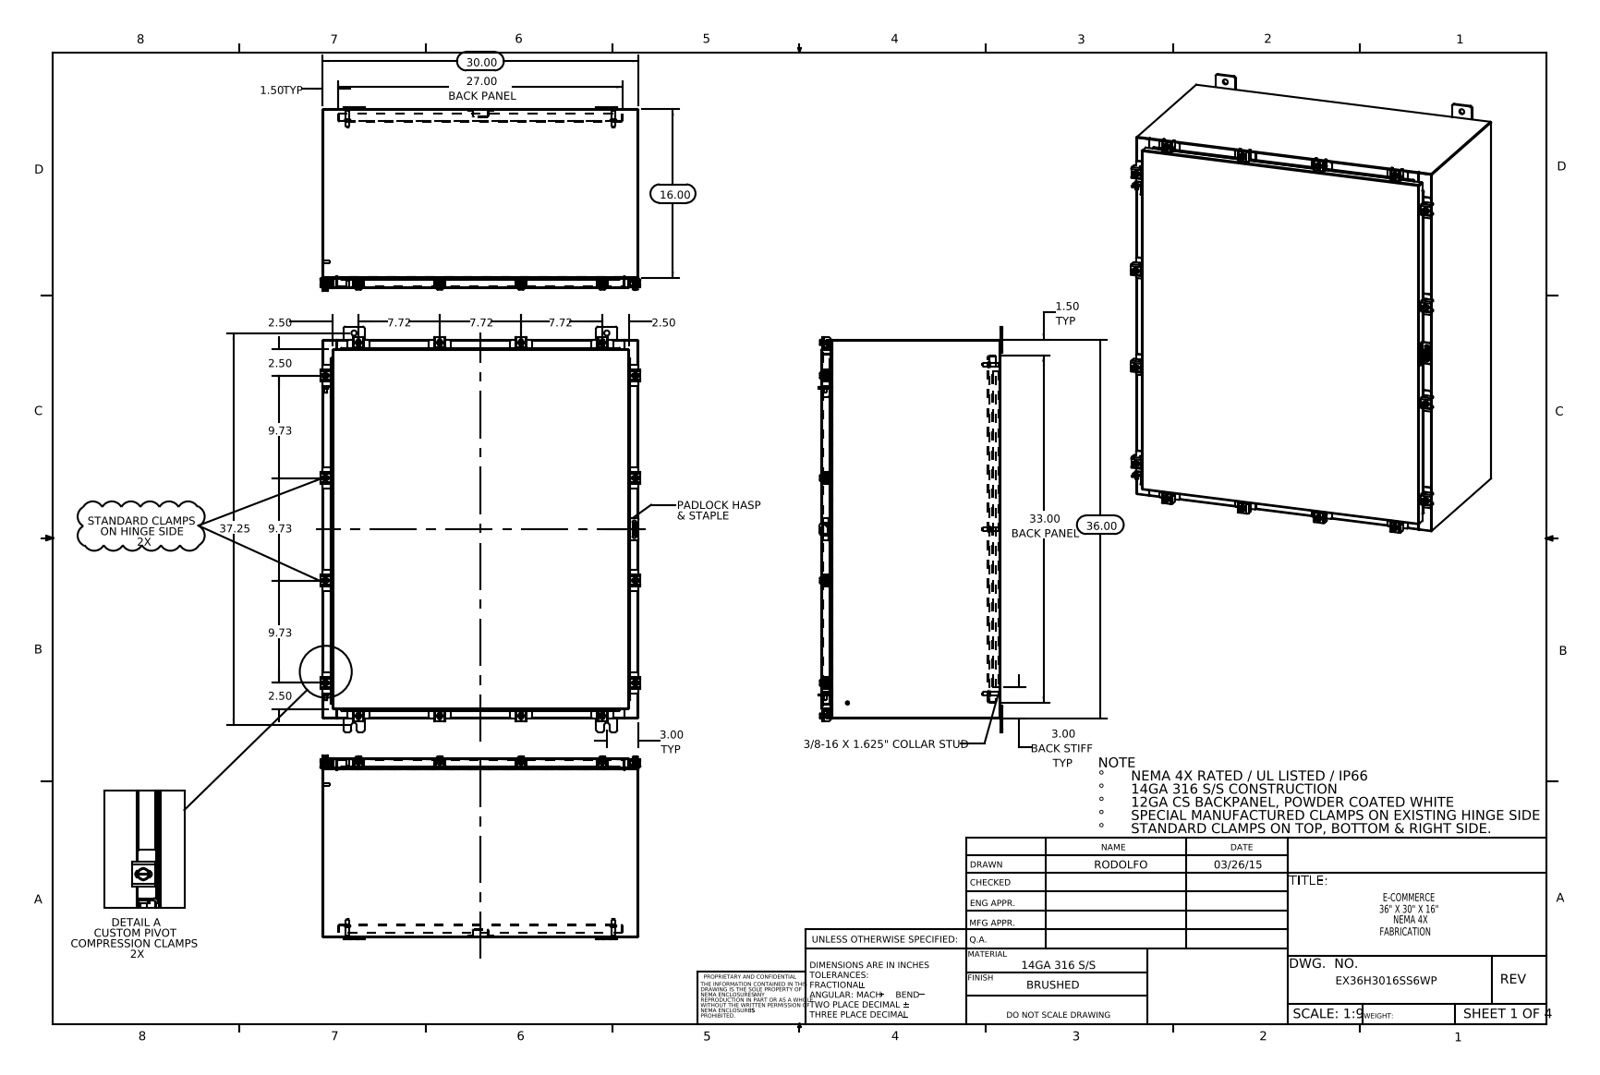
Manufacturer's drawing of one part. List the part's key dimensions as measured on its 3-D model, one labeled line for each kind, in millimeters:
Part name (STEP PRODUCT): 22101002_RTP29; EX36H3016SS6WP Top; EX36H3016SS6WP Mounting Studs; EX36H3016SS6WP Padlock Hasp (+8 more)
STEP written by: SolidWorks 2014 (CONFIG_CONTROL_DESIGN)
Units: millimetres
Bodies: 104 solids, 2594 faces (1371 planar, 1011 cylindrical, 212 other)
Overall size (bounding box): 977.9 × 772.7 × 443.3
Volume: 7 536 000 mm³ · Surface area: 7 450 000 mm²
Round holes (diameter × count): ⌀5.4 ×16, ⌀6.6 ×16, ⌀12.7 ×10, ⌀3.2 ×1, ⌀6.4 ×1
Round bosses / shafts (diameter × count): ⌀12.7 ×16, ⌀6.4 ×16, ⌀10.1 ×14, ⌀15.9 ×6, ⌀9.5 ×6, ⌀8.4 ×6, ⌀8 ×2, ⌀6 ×2
Partial cylindrical surfaces — rounded edges, fillets, slot ends (radius × count): R1.5 ×70, R3.6 ×32, R0.3 ×30, R3 ×30, R2.2 ×26, R4.8 ×24, R2.3 ×22, R1.3 ×21
Main face-to-face distances: 1.9, 429.3, 760.1, 427.4, 431.2, 2.6, 912.5, 25.4, 27.3, 402
Hole centre spacings: 787.8, 59.6, 112.8, 134.6, 247.1, 278.5, 336.3, 374.5
